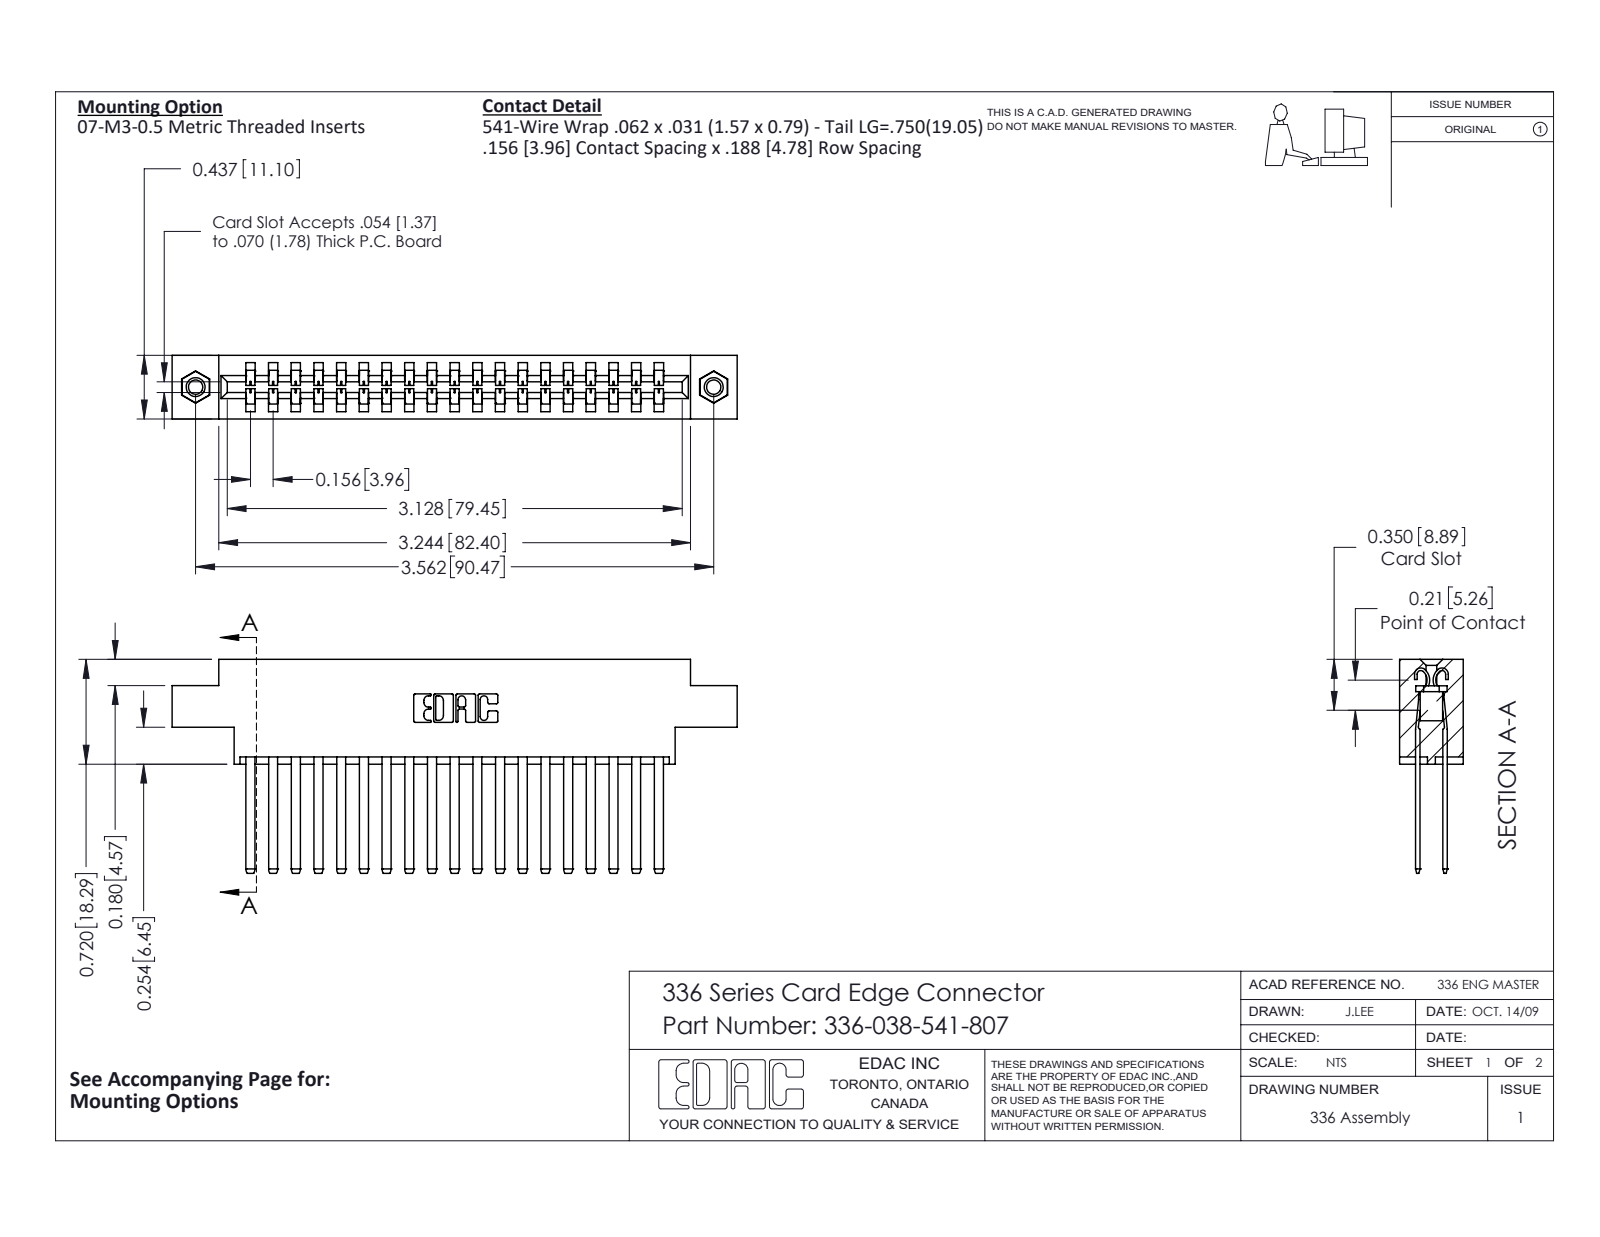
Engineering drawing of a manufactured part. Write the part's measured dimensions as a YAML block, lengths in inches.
part_name: "336 Part_Offset - .156 Dia - TI; 336-038-541-807; 345-250-001_345-250-005-103; 336-290-001_336-290-541"
step_written_by: "SolidWorks 2020 (CONFIG_CONTROL_DESIGN)"
units: inches
bodies: {solids: 41, faces: 1774, planar: 1094, cylindrical: 664, other: 16}
overall_size: [3.885, 1.47, 0.437]
volume: 0.883
surface_area: 28.12
round_holes:
  - {diameter: 0.098, count: 2}
  - {diameter: 0.125, count: 2}
  - {diameter: 0.156, count: 2}
round_bosses_or_shafts:
  - {diameter: 0.155, count: 2}
partial_cylinders:
  - {radius: 0.004, count: 76}
  - {radius: 0.056, count: 38}
  - {radius: 0.01, count: 22}
  - {radius: 0.007, count: 6}
  - {radius: 0.031, count: 6}
  - {radius: 0.022, count: 4}
  - {radius: 0.04, count: 4}
  - {radius: 0.026, count: 3}
face_to_face_distances: [0.188, 0.328, 0.14, 0.297, 0.109, 0.031, 0.437, 0.033, 0.181, 0.146]
hole_center_spacings: [3.562]
